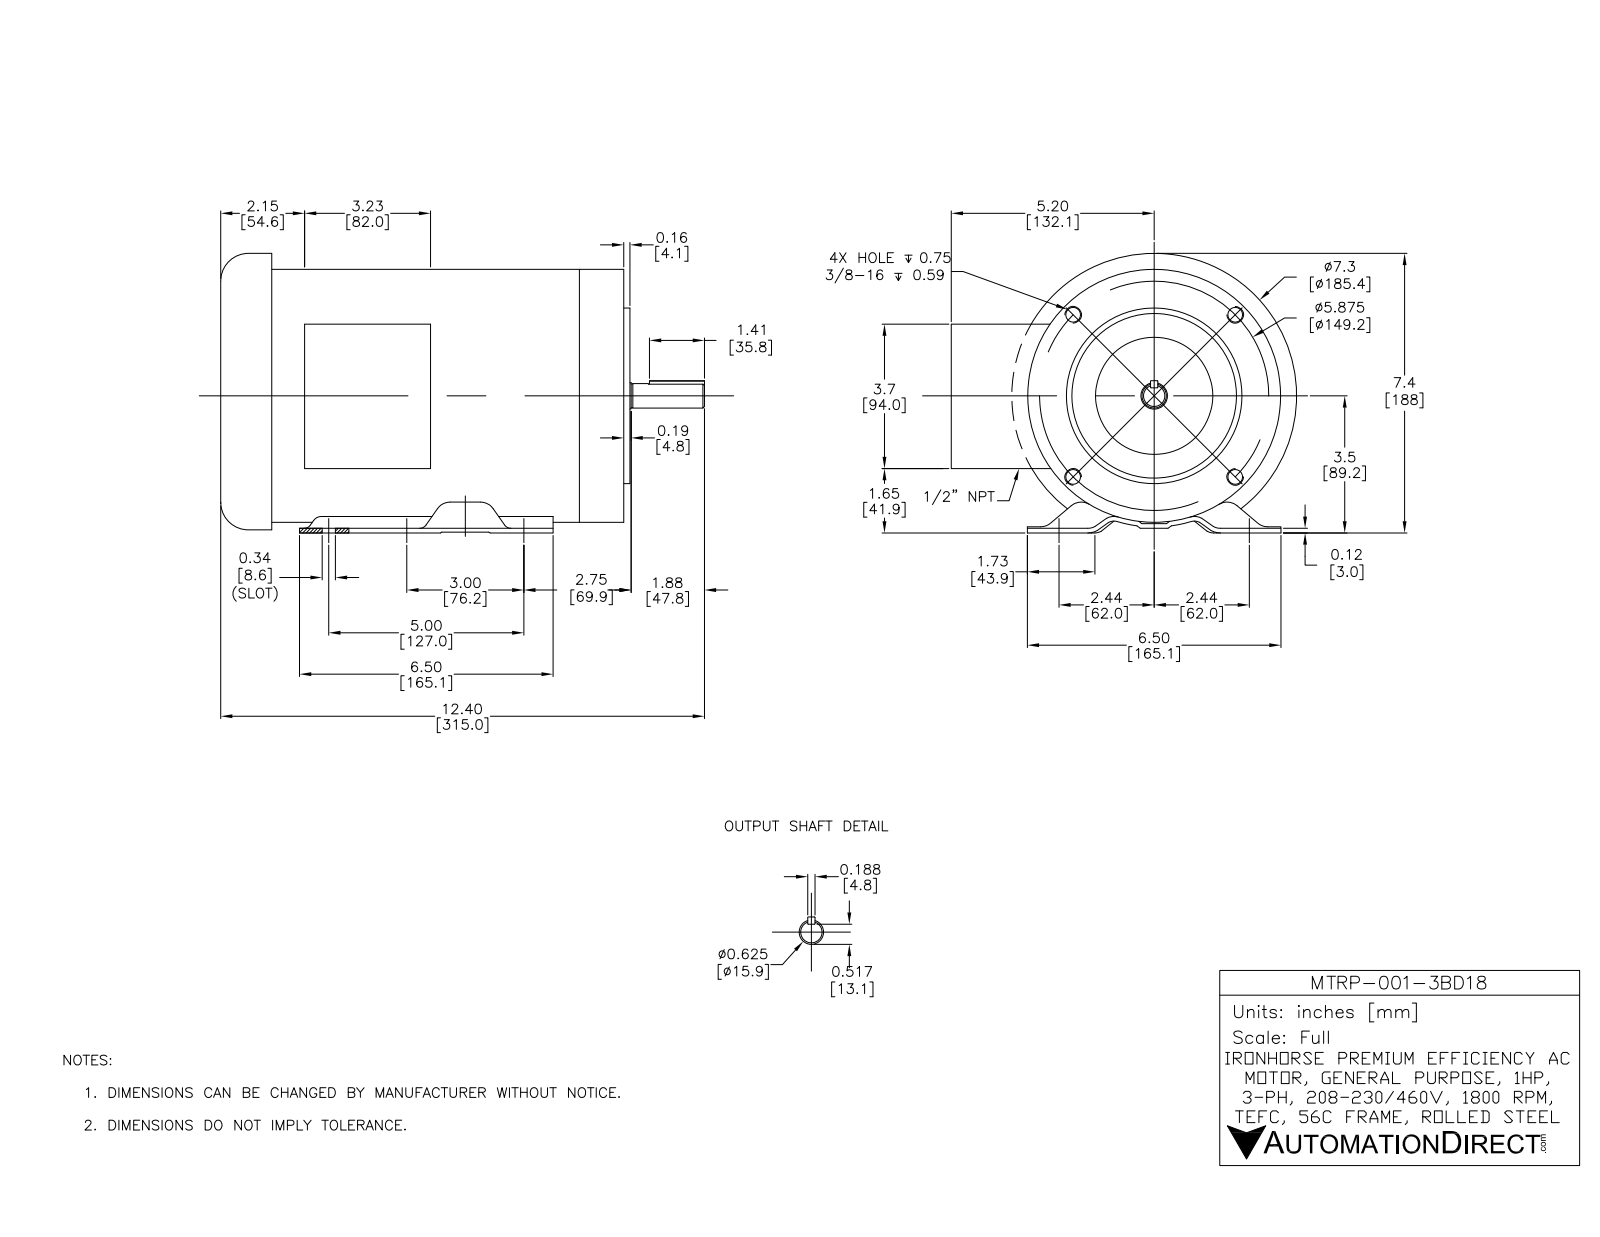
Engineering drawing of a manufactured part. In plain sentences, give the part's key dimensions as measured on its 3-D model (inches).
The part is named "MTRP-001-3BD18". Its 3-D file was written by "SolidWorks 2021 (AUTOMOTIVE_DESIGN)". It is 39 solids with 3607 faces: 797 planar, 1141 cylindrical and 1669 other. Overall it measures 12.224 by 8.938 by 7.234 inches. Its volume is 45.11 cubic inches and its surface area 979.4 square inches. Round holes: 12 of diameter 0.197, 9 of diameter 0.219, 8 of diameter 0.276, 6 of diameter 0.217, 6 of diameter 0.273, 6 of diameter 0.344, 5 of diameter 0.136, 4 of diameter 0.15, 4 of diameter 0.177, 4 of diameter 0.313, 2 of diameter 0.067, 2 of diameter 0.134. Round bosses or shafts: 9 of diameter 0.164, 7 of diameter 0.348, 6 of diameter 0.414, 6 of diameter 0.25, 6 of diameter 0.19, 2 of diameter 0.348, 1 of diameter 7.185, 1 of diameter 6.457. Partial cylindrical surfaces (rounded edges, fillets, slot ends): 204 of radius 0.02, 123 of radius 0.118, 43 of radius 0.079, 38 of radius 0.039, 32 of radius 0.157, 26 of radius 0.138, 19 of radius 0.276, 12 of radius 0.172. The main face-to-face distances are 0.118, 0.039, 0.063, 10.157, 10.118, 3.559, 0.079, 3.087, 0.047, 0.098. The hole center spacings are 4.221, 3.031, 0.094, 2.32, 2.409, 2.937, 2.979, 3.748.
